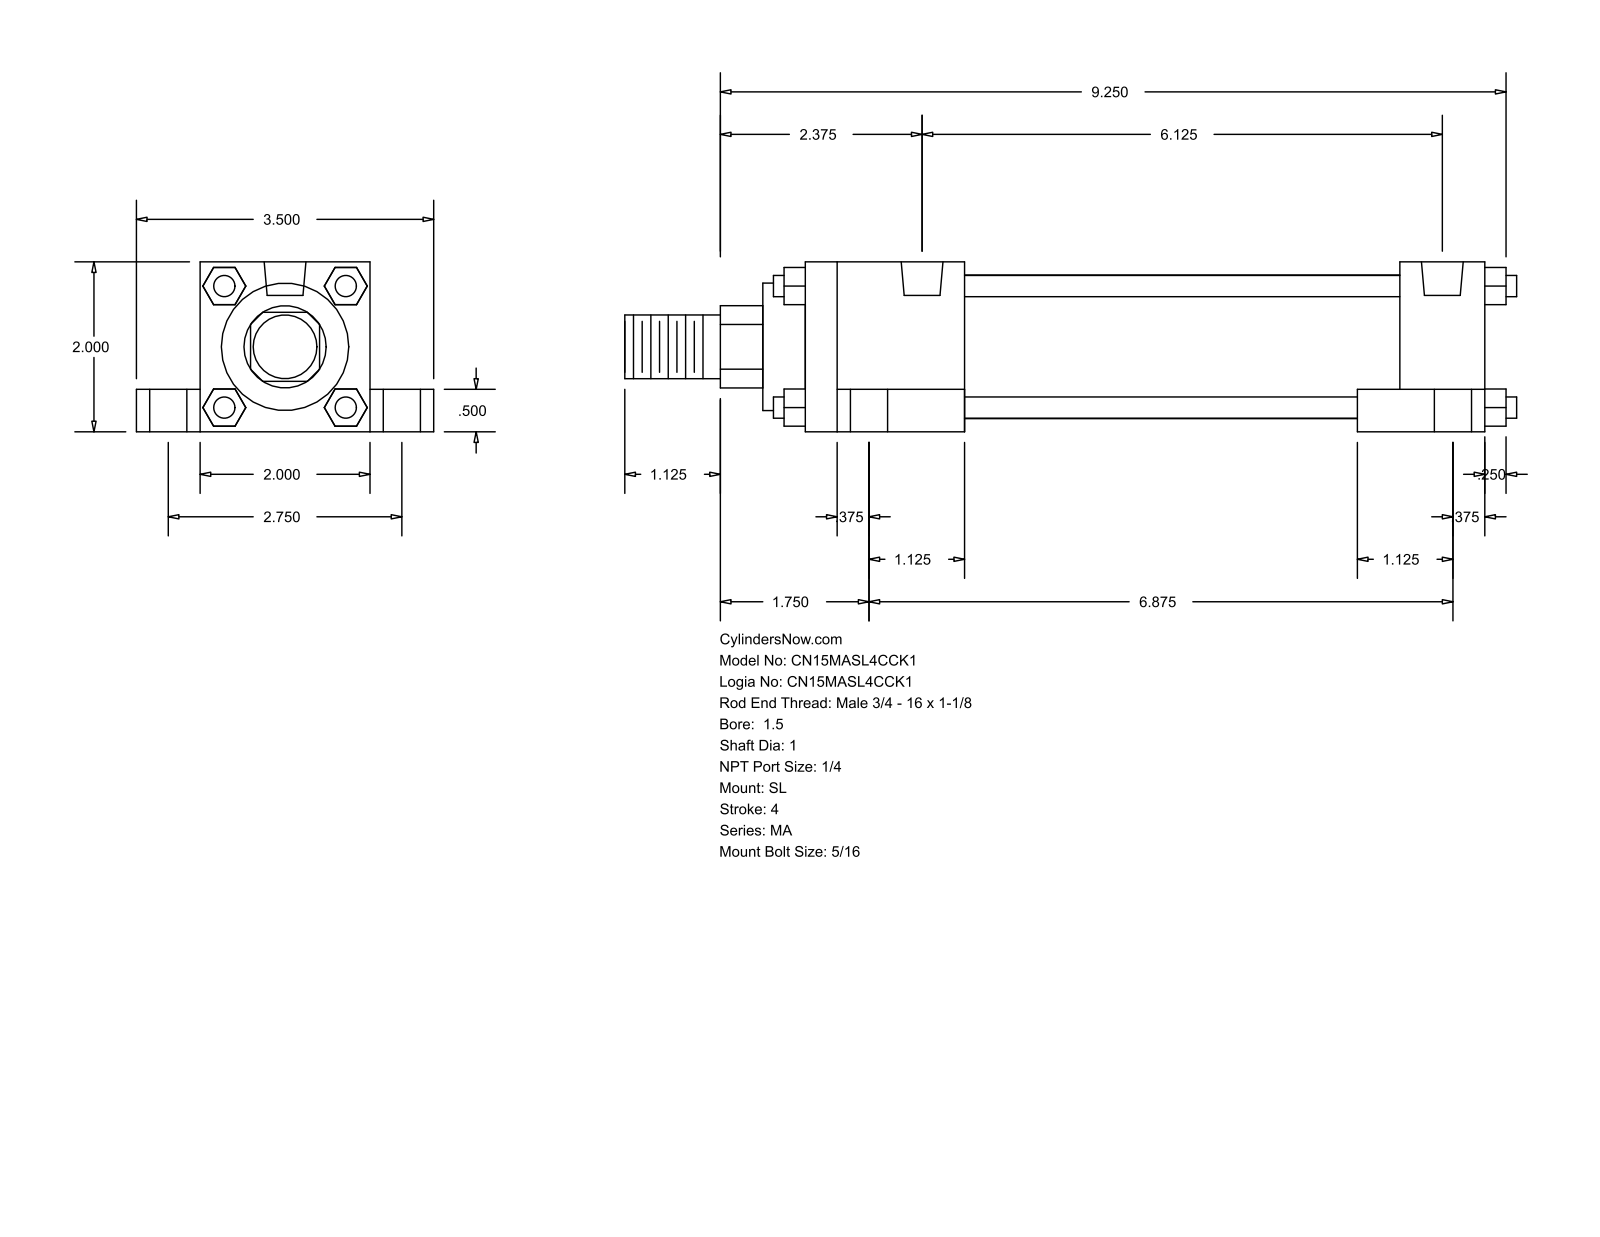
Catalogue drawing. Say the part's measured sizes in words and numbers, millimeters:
The part is named "MA_SL__0150_1". Its 3-D file was written by "GSSL Pune (CONFIG_CONTROL_DESIGN)". It is 0 solids with 148 faces: 112 planar, 36 cylindrical and 0 other. Overall it measures 266.7 by 88.9 by 50.8 millimeters. Round holes: 4 of diameter 7.94, 4 of diameter 11.11, 4 of diameter 17.46, 2 of diameter 12.49. Round bosses or shafts: 4 of diameter 6.35, 1 of diameter 42.93, 1 of diameter 38.1, 1 of diameter 25.4, 1 of diameter 19.05. Partial cylindrical surfaces (rounded edges, fillets, slot ends): 1 of radius 12.29. The main face-to-face distances are 50.8, 12.7, 19.05, 69.85, 38.1, 9.52, 203.2, 25.4, 6.35, 177.8. The hole center spacings are 35.06, 38.36, 69.84, 155.57, 162.54, 174.62, 174.97, 188.07.
